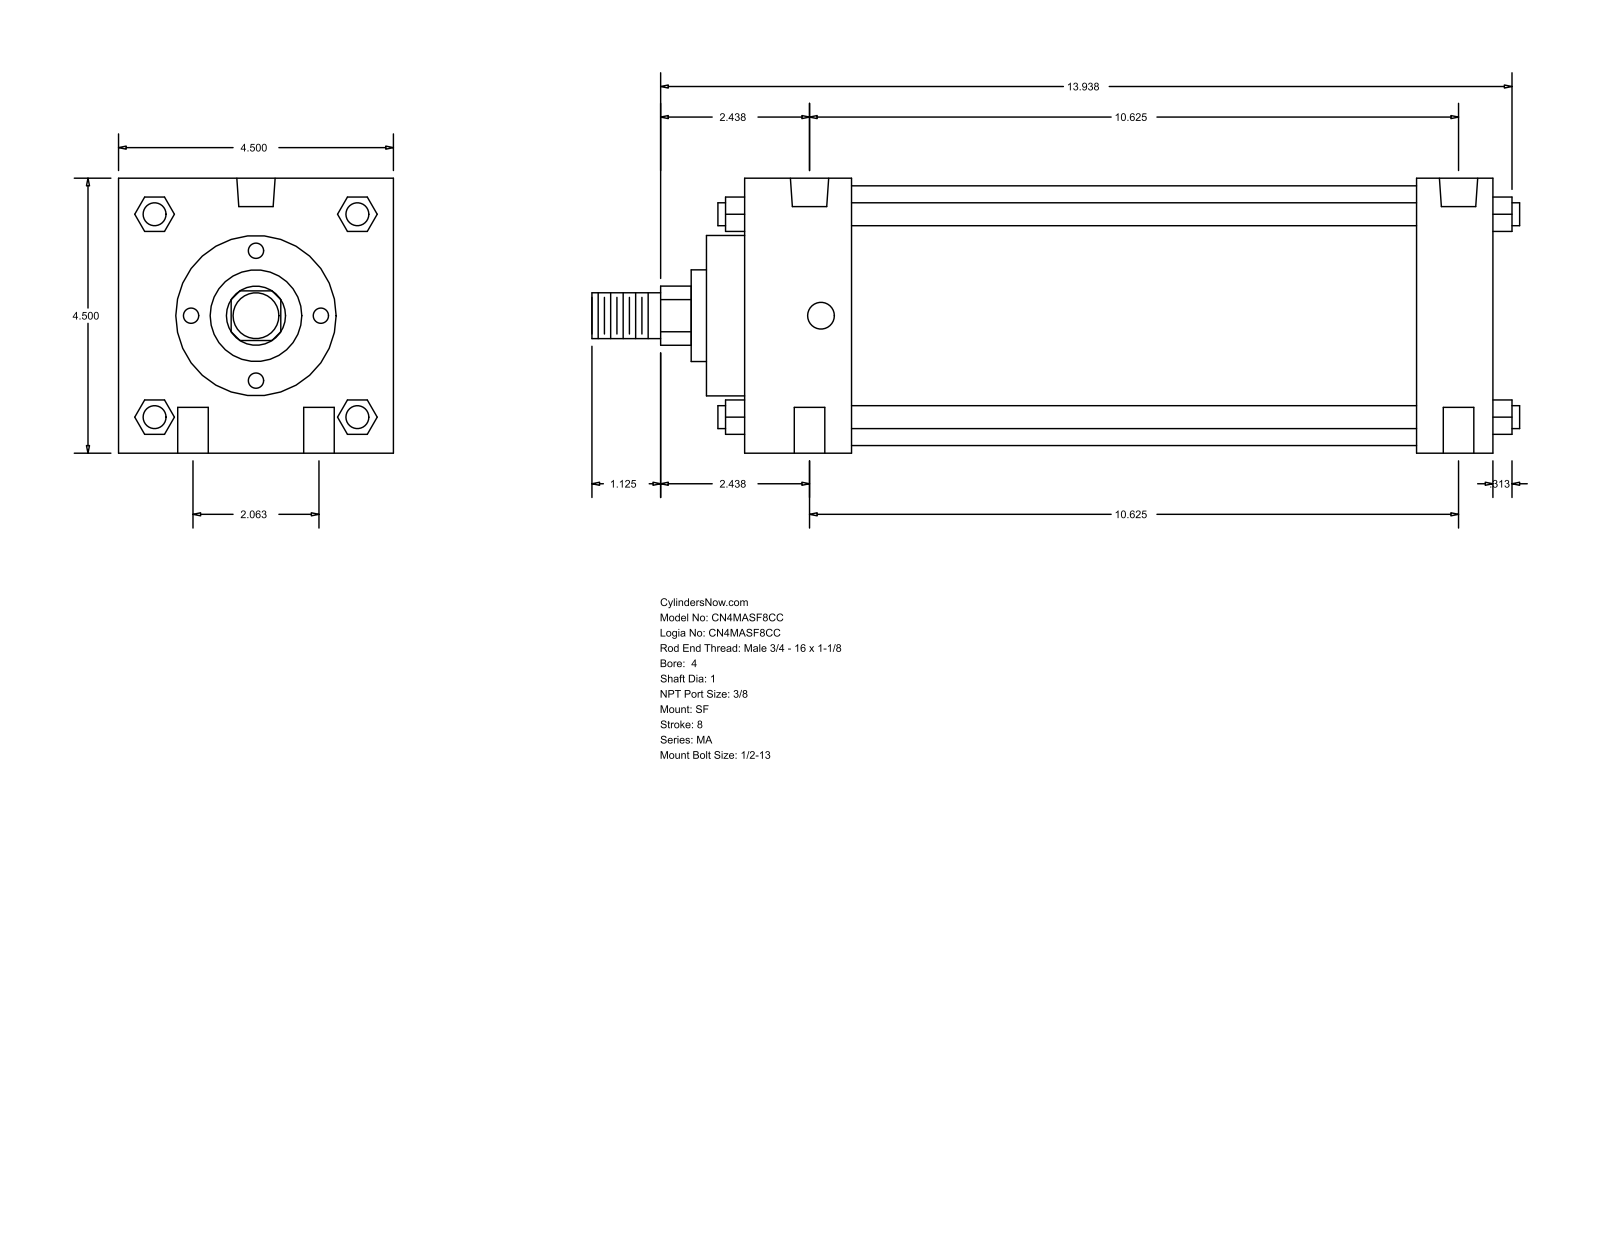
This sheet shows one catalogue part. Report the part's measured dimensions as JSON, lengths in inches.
{"part_name": "MA_SF__0400_1", "step_written_by": "GSSL Pune (CONFIG_CONTROL_DESIGN)", "units": "inches", "bodies": {"solids": 0, "faces": 126, "planar": 95, "cylindrical": 31, "other": 0}, "overall_size": [15.187, 4.5, 4.5], "round_holes": [[0.5, 4], [0.437, 2], [0.627, 2]], "round_bosses_or_shafts": [[0.375, 4], [4.25, 1], [2.625, 1], [1.5, 1], [1, 1], [0.75, 1]], "partial_cylinders_radius": [[0.484, 1]], "face_to_face_distances": [4.5, 12.25, 11, 1.25, 1.75, 9.25, 10.5, 12.875, 0.625, 2.375], "hole_center_spacings": [1.031, 10.675, 10.625, 2.062, 10.824, 10.25]}
